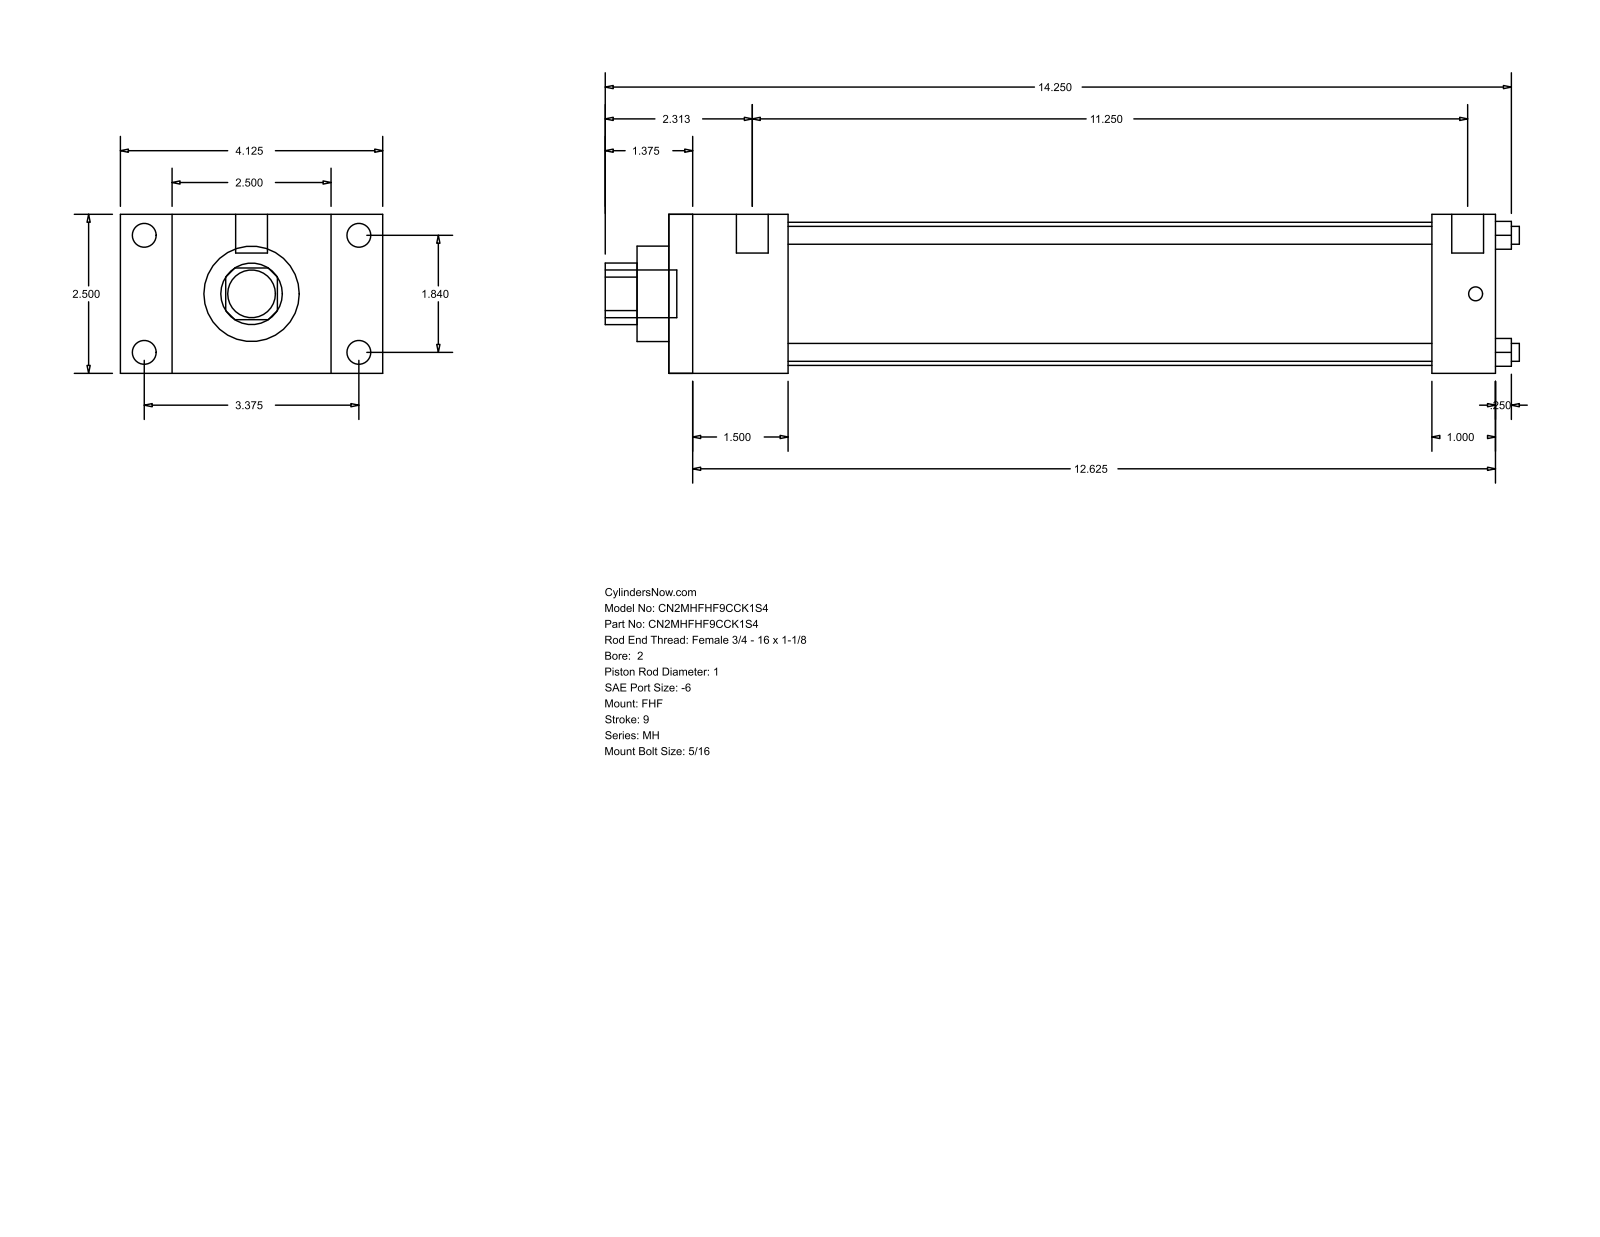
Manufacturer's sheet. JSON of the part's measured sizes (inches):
{"part_name": "MH_FHF__0200_1", "step_written_by": "GSSL Pune (CONFIG_CONTROL_DESIGN)", "units": "inches", "bodies": {"solids": 0, "faces": 88, "planar": 60, "cylindrical": 28, "other": 0}, "overall_size": [14.375, 4.125, 2.5], "round_holes": [[0.281, 4], [1, 1], [1.5, 1], [2.25, 1]], "round_bosses_or_shafts": [[0.375, 4], [0.219, 4], [0.5, 2], [0.75, 1]], "partial_cylinders_radius": [[0.484, 1]], "face_to_face_distances": [2.5, 13, 1.875, 11.125, 0.813, 3.313, 4.125, 1, 12, 10.125], "hole_center_spacings": [1.301, 1.84, 2.602]}
